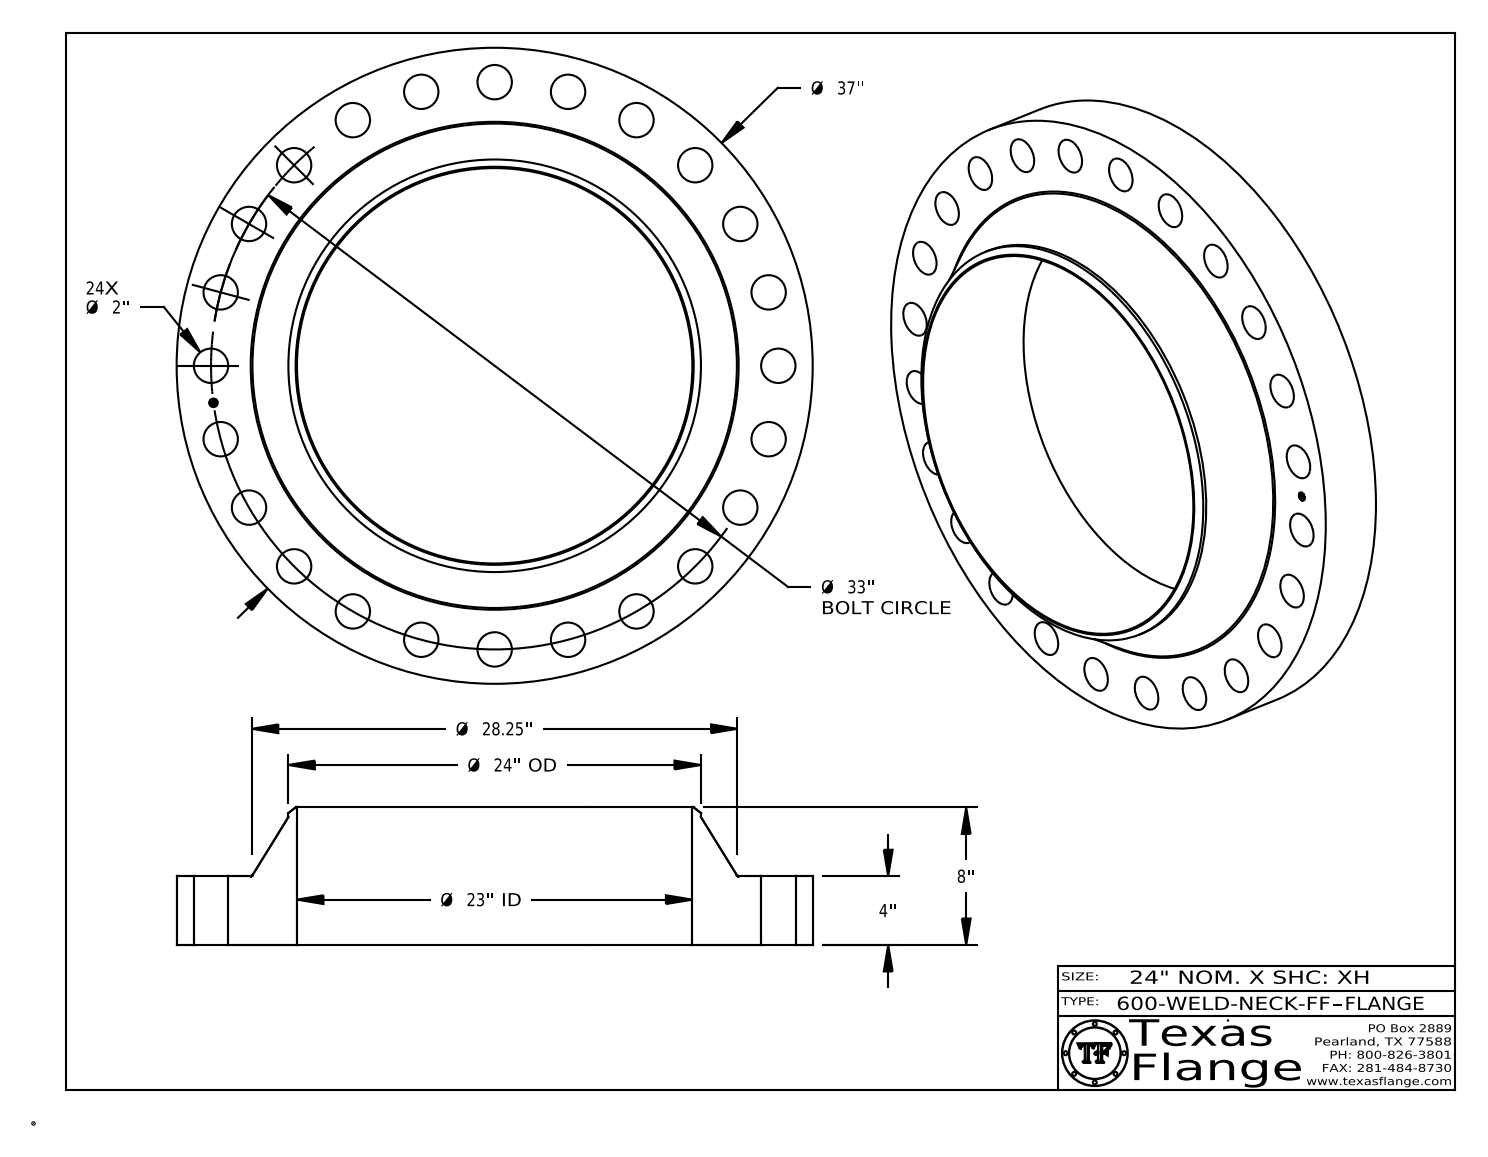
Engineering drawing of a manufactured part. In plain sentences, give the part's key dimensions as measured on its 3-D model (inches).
The part is named "600-WELD-NECK-FF". Its 3-D file was written by "CATIA V5 STEP AP214 (AUTOMOTIVE_DESIGN)". It is 1 solid with 448 faces: 368 planar, 74 cylindrical and 6 other. Overall it measures 37 by 37 by 8 inches. Its volume is 2 772 cubic inches and its surface area 2 997 square inches. Round holes: 24 of diameter 2, 1 of diameter 0.495, 1 of diameter 23. Round bosses or shafts: 8 of diameter 0.03, 1 of diameter 37, 1 of diameter 24, 1 of diameter 0.39. The main face-to-face distances are 4, 8, 0.015, 3.985, 4.015, 0.07, 0.148, 0.144, 0.027, 0.096. The hole center spacings are 16.5, 4.307, 8.541, 20.089, 23.335, 26.181, 31.876, 32.718.
